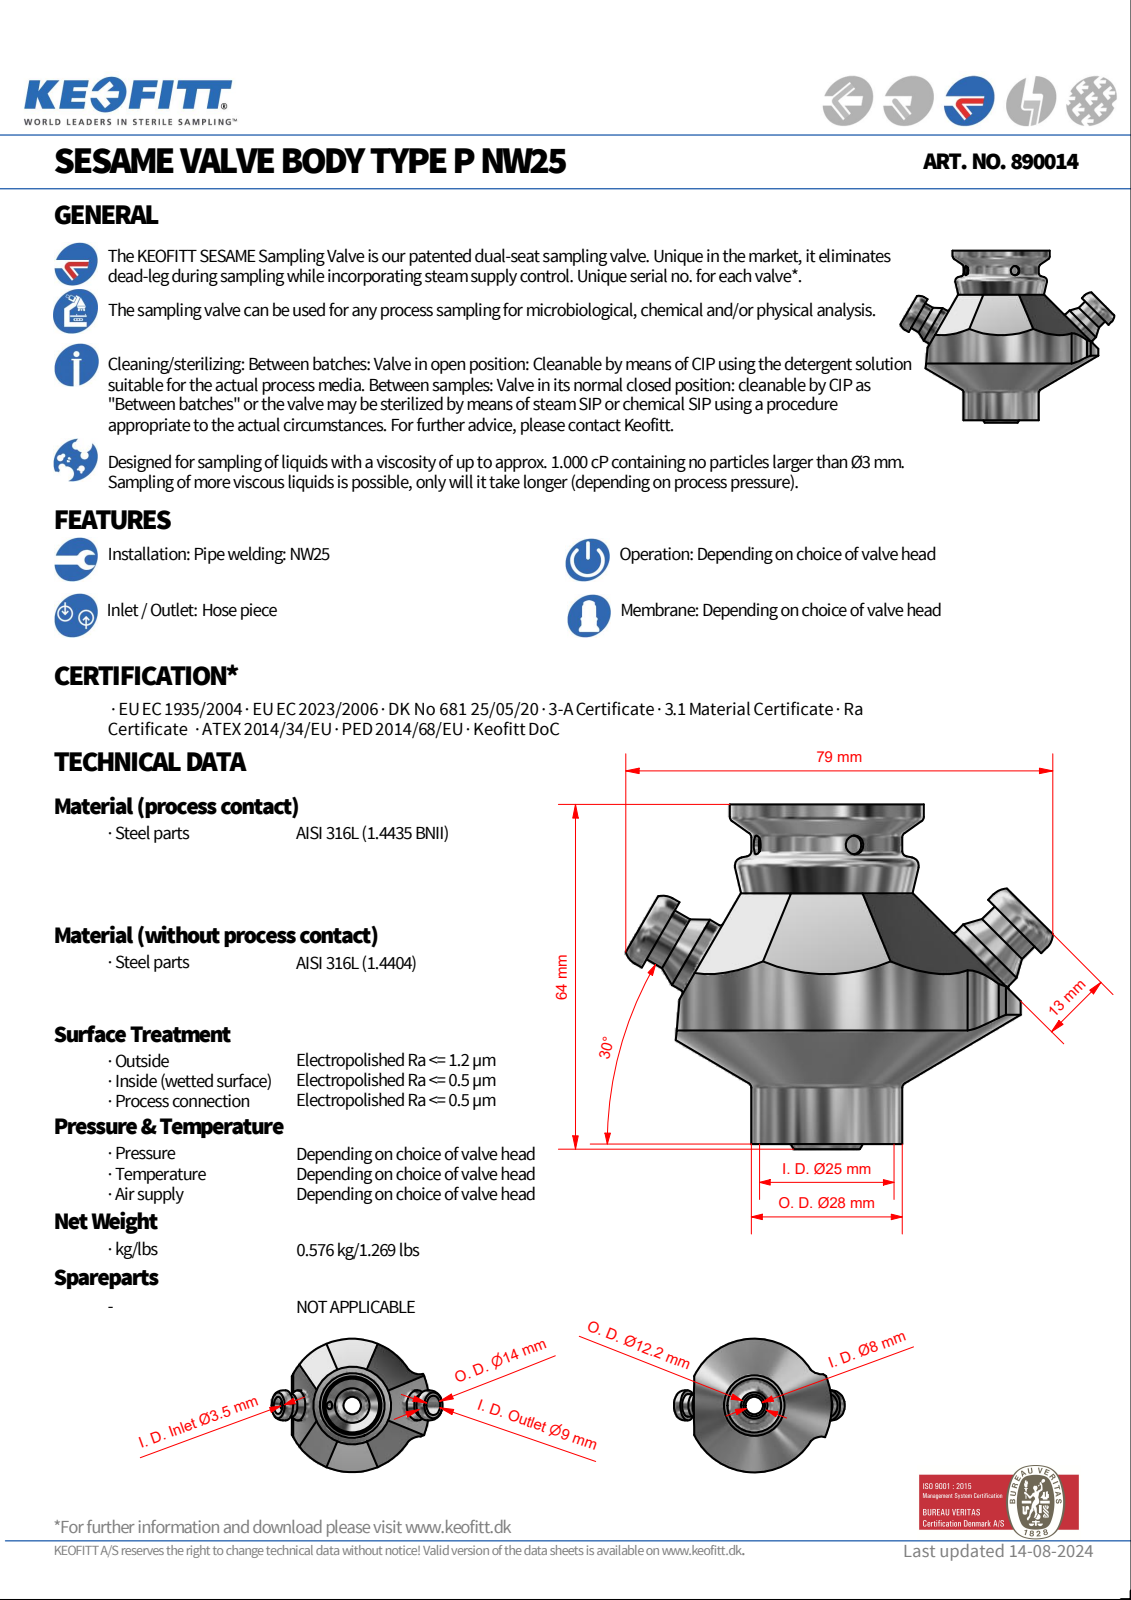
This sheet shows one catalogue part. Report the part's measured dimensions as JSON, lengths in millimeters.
{"part_name": "890514", "step_written_by": "Autodesk Inventor 2022 (AUTOMOTIVE_DESIGN)", "units": "millimeters", "bodies": {"solids": 1, "faces": 59, "planar": 18, "cylindrical": 25, "other": 16}, "overall_size": [79.23, 64, 62], "volume_mm3": 99233, "surface_area_mm2": 14009, "round_holes": [[3.5, 2]], "round_bosses_or_shafts": [[14, 2], [10.5, 2], [36, 1], [28, 1]], "partial_cylinders_radius": [[7, 2], [13, 1], [31, 1], [36, 1]], "face_to_face_distances": [63, 4, 1, 64, 13, 13.01, 9, 9.01, 47.5, 46.5]}
